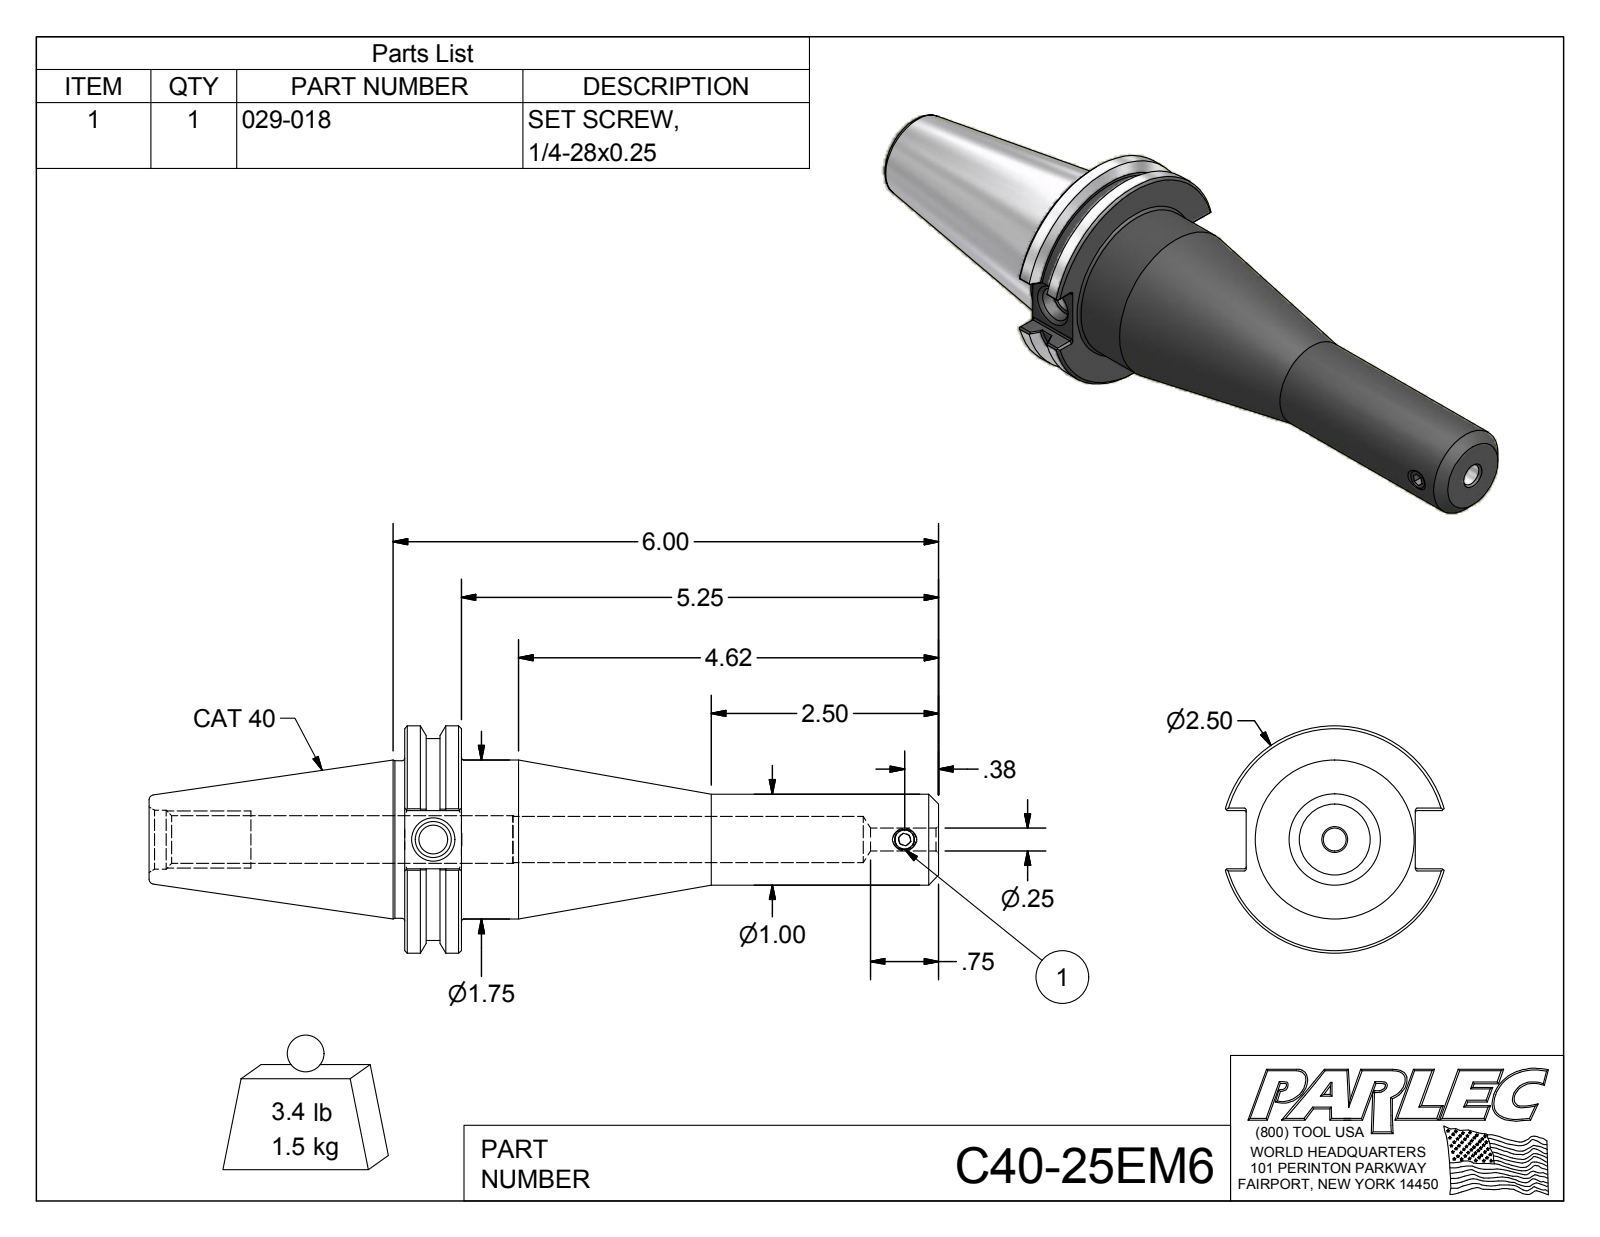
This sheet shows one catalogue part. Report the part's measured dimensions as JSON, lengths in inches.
{"part_name": "C40-25EM6; C40-25EM6-1; 029-018", "step_written_by": "Autodesk Inventor 2012 (AUTOMOTIVE_DESIGN)", "units": "inches", "bodies": {"solids": 2, "faces": 102, "planar": 40, "cylindrical": 29, "other": 33}, "overall_size": [8.687, 2.5, 2.406], "volume_in3": 11.85, "surface_area_in2": 58.54, "round_holes": [[0.211, 1], [0.25, 1], [0.315, 1], [0.399, 1], [0.51, 1], [0.527, 1], [0.648, 1]], "round_bosses_or_shafts": [[2.5, 1], [2.219, 1], [1.75, 1], [1.73, 1], [1, 1], [0.25, 1]], "partial_cylinders_radius": [[0.02, 12]], "face_to_face_distances": [0.625, 5.875, 5.25, 0.64, 1.86, 2.812, 3.437, 8.687, 3.201, 0.389], "hole_center_spacings": [5.185]}
